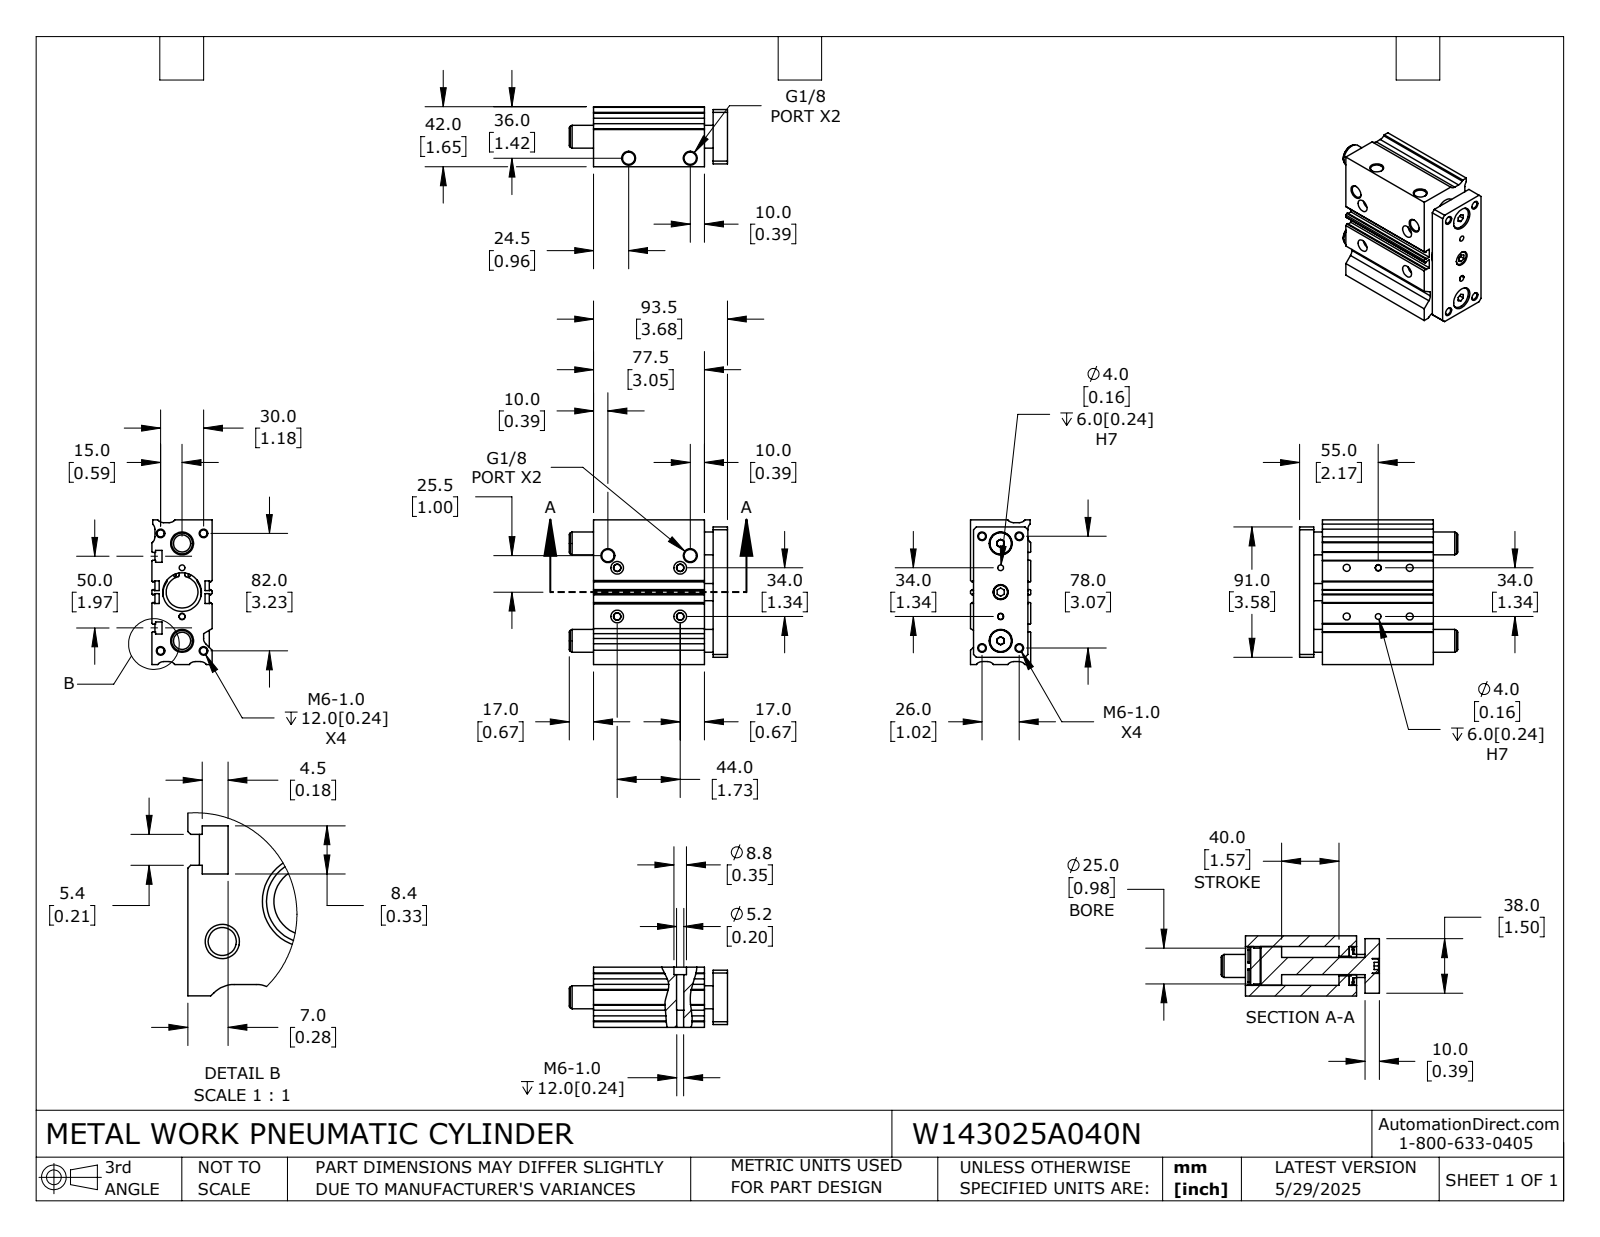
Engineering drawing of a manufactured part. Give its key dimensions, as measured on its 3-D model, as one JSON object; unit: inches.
{"part_name": "W143025A040N_ROD; W143025A040N; W143025A040N_BODY", "step_written_by": "SolidWorks 2024 (CONFIG_CONTROL_DESIGN)", "units": "inches", "bodies": {"solids": 6, "faces": 390, "planar": 191, "cylindrical": 157, "other": 42}, "overall_size": [4.35, 3.976, 1.654], "volume_in3": 19.15, "surface_area_in2": 131.9, "round_holes": [[0.194, 8], [0.067, 4], [0.157, 4], [0.194, 4], [0.205, 4], [0.337, 4], [0.346, 4], [0.63, 2], [0.413, 1], [0.472, 1], [0.539, 1], [0.874, 1]], "round_bosses_or_shafts": [[0.61, 2], [1.063, 1], [0.984, 1], [0.65, 1], [0.394, 1]], "partial_cylinders_radius": [[0.039, 12], [0.197, 9], [0.079, 8], [0.524, 2], [0.559, 1]], "face_to_face_distances": [0.197, 0.079, 1.654, 1.378, 0.236, 0.118, 0.63, 0.394, 3.681, 3.287], "hole_center_spacings": [1.339, 0.111, 0.29, 0.5, 0.548, 0.652, 0.669, 0.866]}
